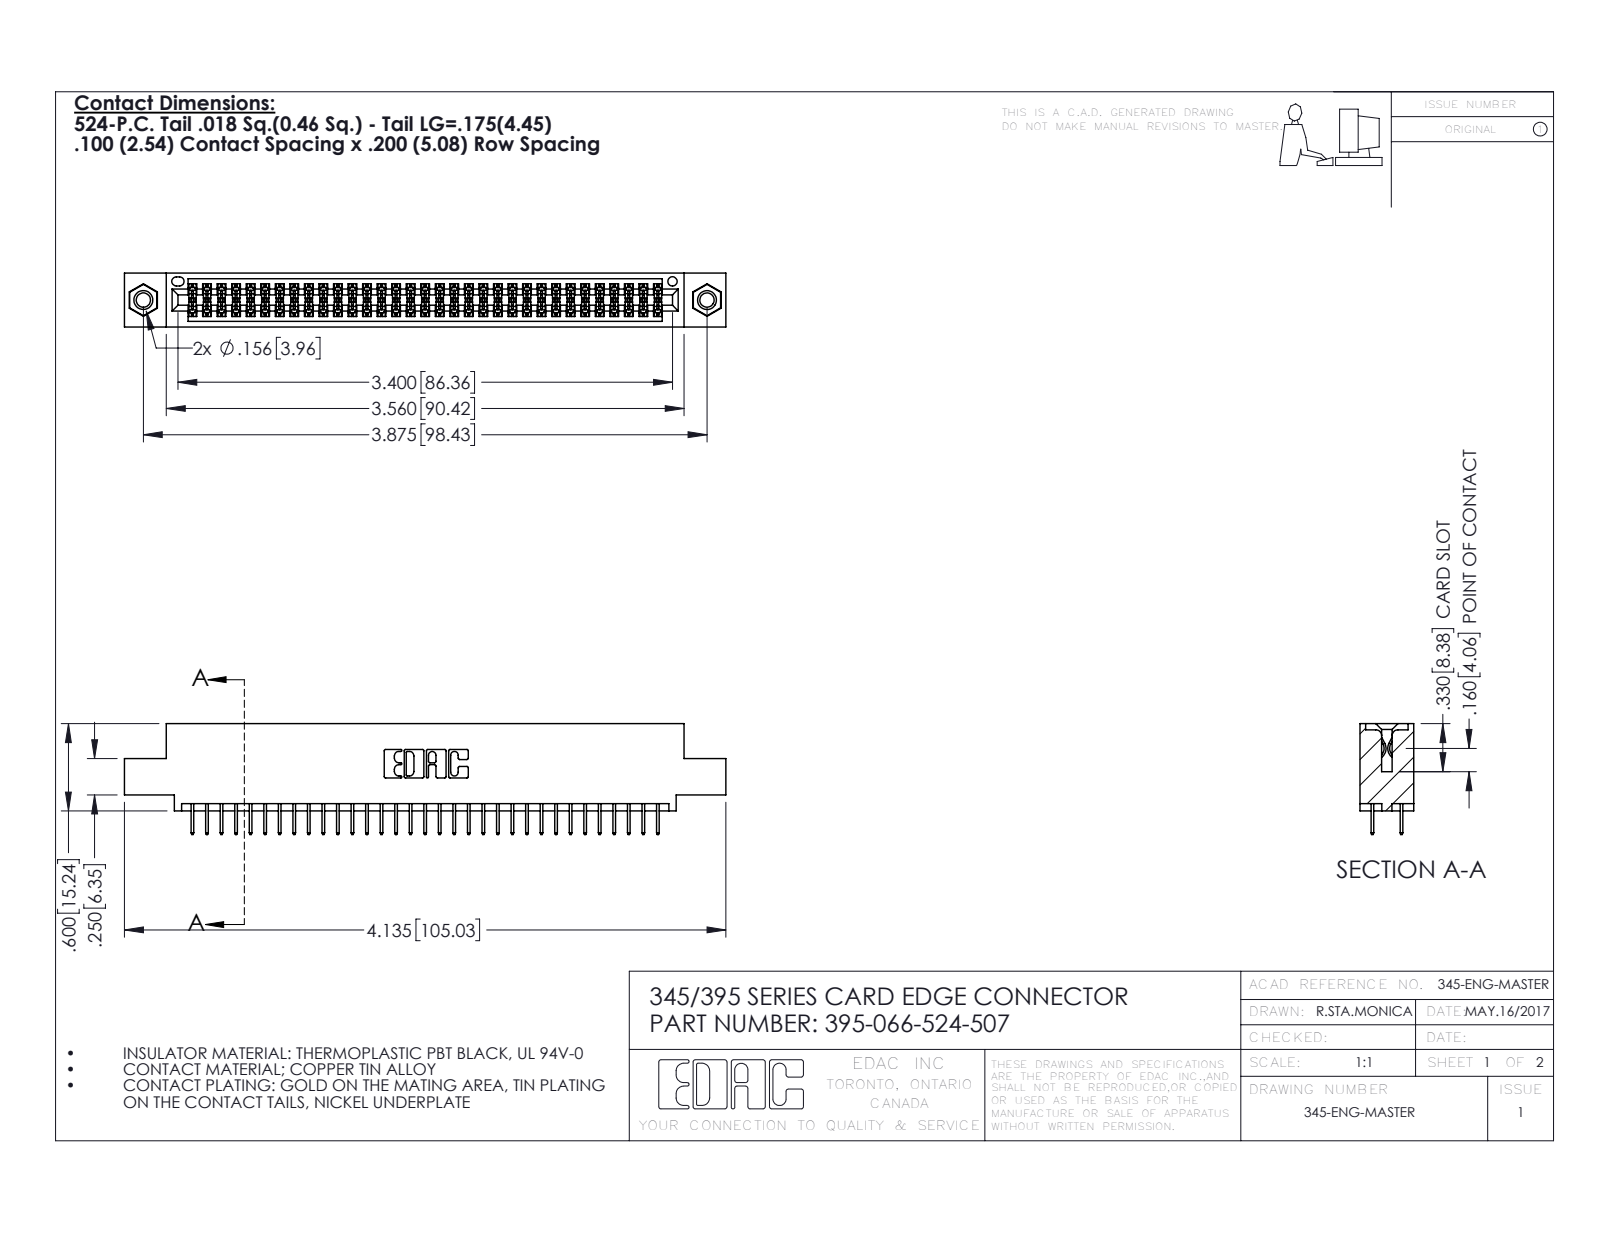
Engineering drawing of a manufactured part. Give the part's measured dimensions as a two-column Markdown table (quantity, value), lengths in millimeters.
| quantity | value |
| --- | --- |
| part name | 345 Part_0.110 Offset - 0.156 Dia-TI; 345-292-001_345-293-124; 345-250-001_345-250-005-103; 395-066-524-507 |
| STEP written by | SolidWorks 2016 (CONFIG_CONTROL_DESIGN) |
| units | millimeters |
| bodies | 69 solids, 3754 faces (2690 planar, 1048 cylindrical, 16 other) |
| overall size | 105 × 19.4 × 9.4 |
| volume | 9 930 mm³ |
| surface area | 14 360 mm² |
| round holes (diameter × count) | 2.5 × 2, 3.2 × 2, 4 × 2, 1.6 × 1 |
| round bosses / shafts (diameter × count) | 3.9 × 2 |
| partial cylindrical surfaces (radius × count) | 0.2 × 99, 0.3 × 22, 0.2 × 6, 0.8 × 6, 0.7 × 3, 0.4 × 2, 0.5 × 2, 0.6 × 2 |
| main face-to-face distances | 1.8, 7.6, 5.1, 9.4, 2.5, 6.9, 0.6, 5.7, 1.8, 4.4 |
| hole center spacings | 6.9, 92.5, 98.4 |
